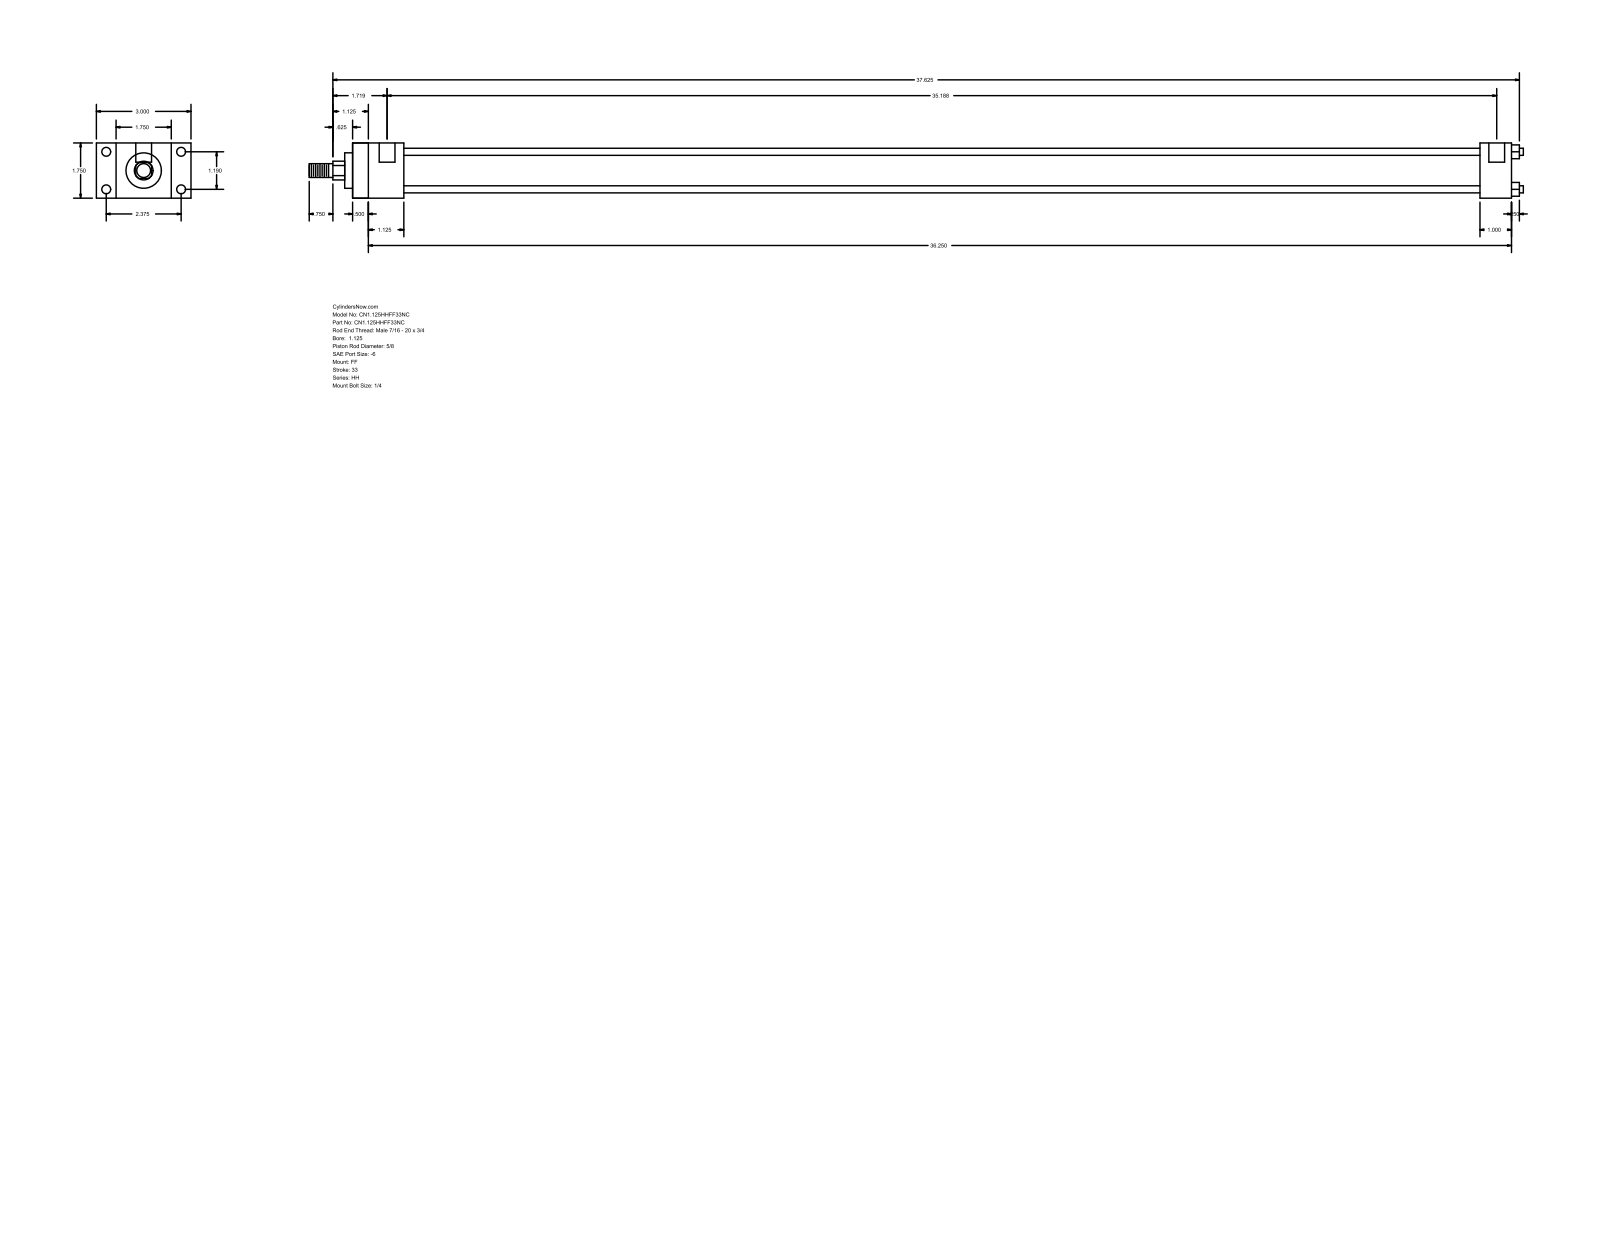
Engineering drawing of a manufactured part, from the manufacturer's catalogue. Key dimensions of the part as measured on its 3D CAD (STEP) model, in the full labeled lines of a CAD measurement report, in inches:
Part name (STEP PRODUCT): HH_FF__0112_0.625
STEP written by: GSSL Pune (CONFIG_CONTROL_DESIGN)
Units: inches
Bodies: 0 solids, 92 faces (64 planar, 28 cylindrical, 0 other)
Overall size (bounding box): 38.5 × 3 × 1.75
Round holes (diameter × count): ⌀0.219 ×4, ⌀0.281 ×4, ⌀0.5 ×2
Round bosses / shafts (diameter × count): ⌀0.225 ×4, ⌀1.375 ×1, ⌀1.125 ×1, ⌀0.625 ×1, ⌀0.437 ×1
Partial cylindrical surfaces — rounded edges, fillets, slot ends (radius × count): R0.297 ×1
Main face-to-face distances: 1.75, 36.75, 0.625, 0.5, 36.25, 1.125, 2.375, 1.625, 35.75, 35.25
Hole centre spacings: 1.19, 2.375, 2.656, 35.063, 0.125, 35.187
